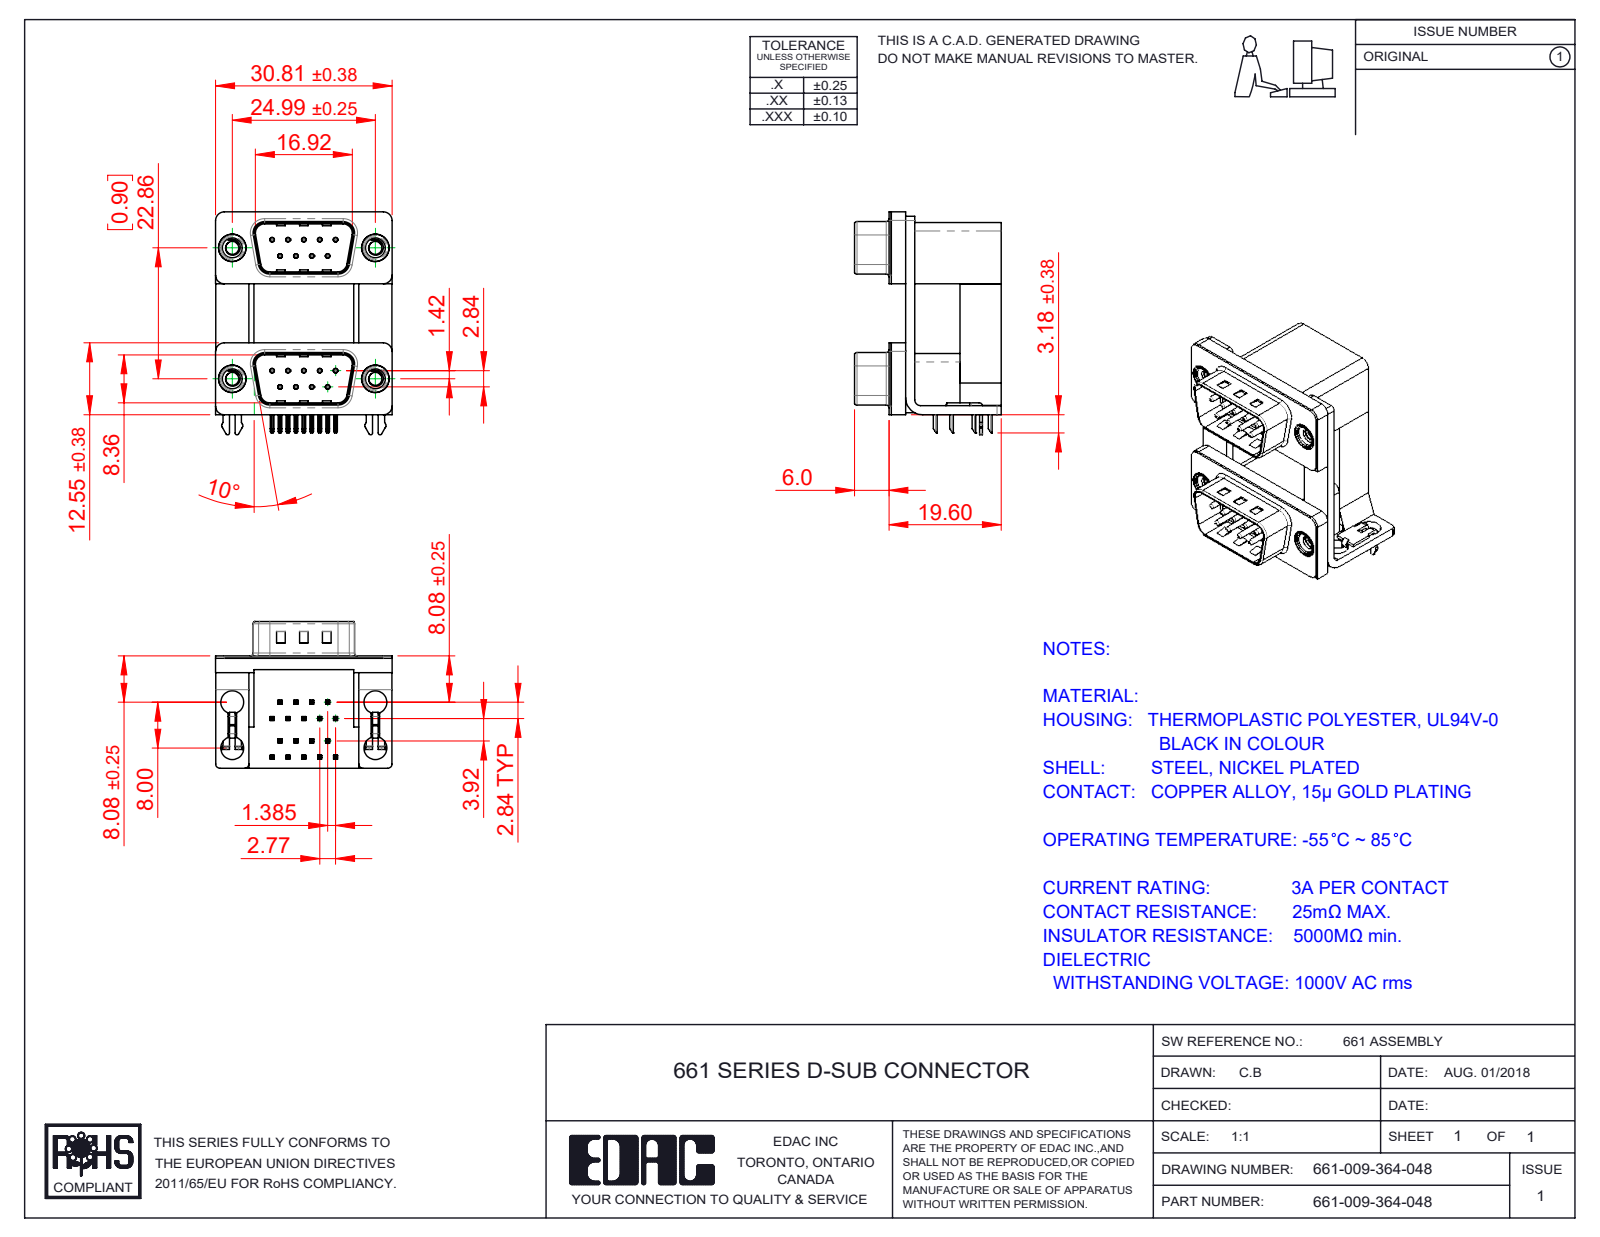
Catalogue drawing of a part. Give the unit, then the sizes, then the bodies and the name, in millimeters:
Units: millimetres
Overall size (bounding box): 38.91 × 30.81 × 25.6
Round holes (diameter × count): ⌀0.35 ×18, ⌀0.8 ×18, ⌀4 ×8, ⌀2.26 ×4, ⌀3.5 ×4, ⌀4.8 ×4, ⌀5 ×4
Round bosses / shafts (diameter × count): ⌀0.75 ×18, ⌀4.9 ×4, ⌀4.75 ×4, ⌀3.9 ×4
Partial cylindrical surfaces — rounded edges, fillets, slot ends (radius × count): R0.25 ×78, R0.12 ×36, R0.5 ×20, R1.5 ×14, R0.75 ×10, R0.9 ×8, R1.6 ×8, R2 ×8
Main face-to-face distances: 0.4, 2.5, 22.86, 12, 16.7, 19.2, 7.2, 9.5, 12.4, 1.6
Hole centre spacings: 3.16, 2.77, 23.03, 22.86, 5.54, 23.52, 20.07, 25.74
Volume: 10 823 mm³ · Surface area: 12 488 mm²
Bodies: 31 solids, 2056 faces (1230 planar, 624 cylindrical, 202 other)
Part name (STEP PRODUCT): 661 Mounting Bracket_2ProngH; 661 Housing Upper_09 Contacts H; 661 Threaded Rivet_4-40; 661 2 Prong Board Lock_4 (+8 more)
STEP written by: SolidWorks 2020 (CONFIG_CONTROL_DESIGN)
